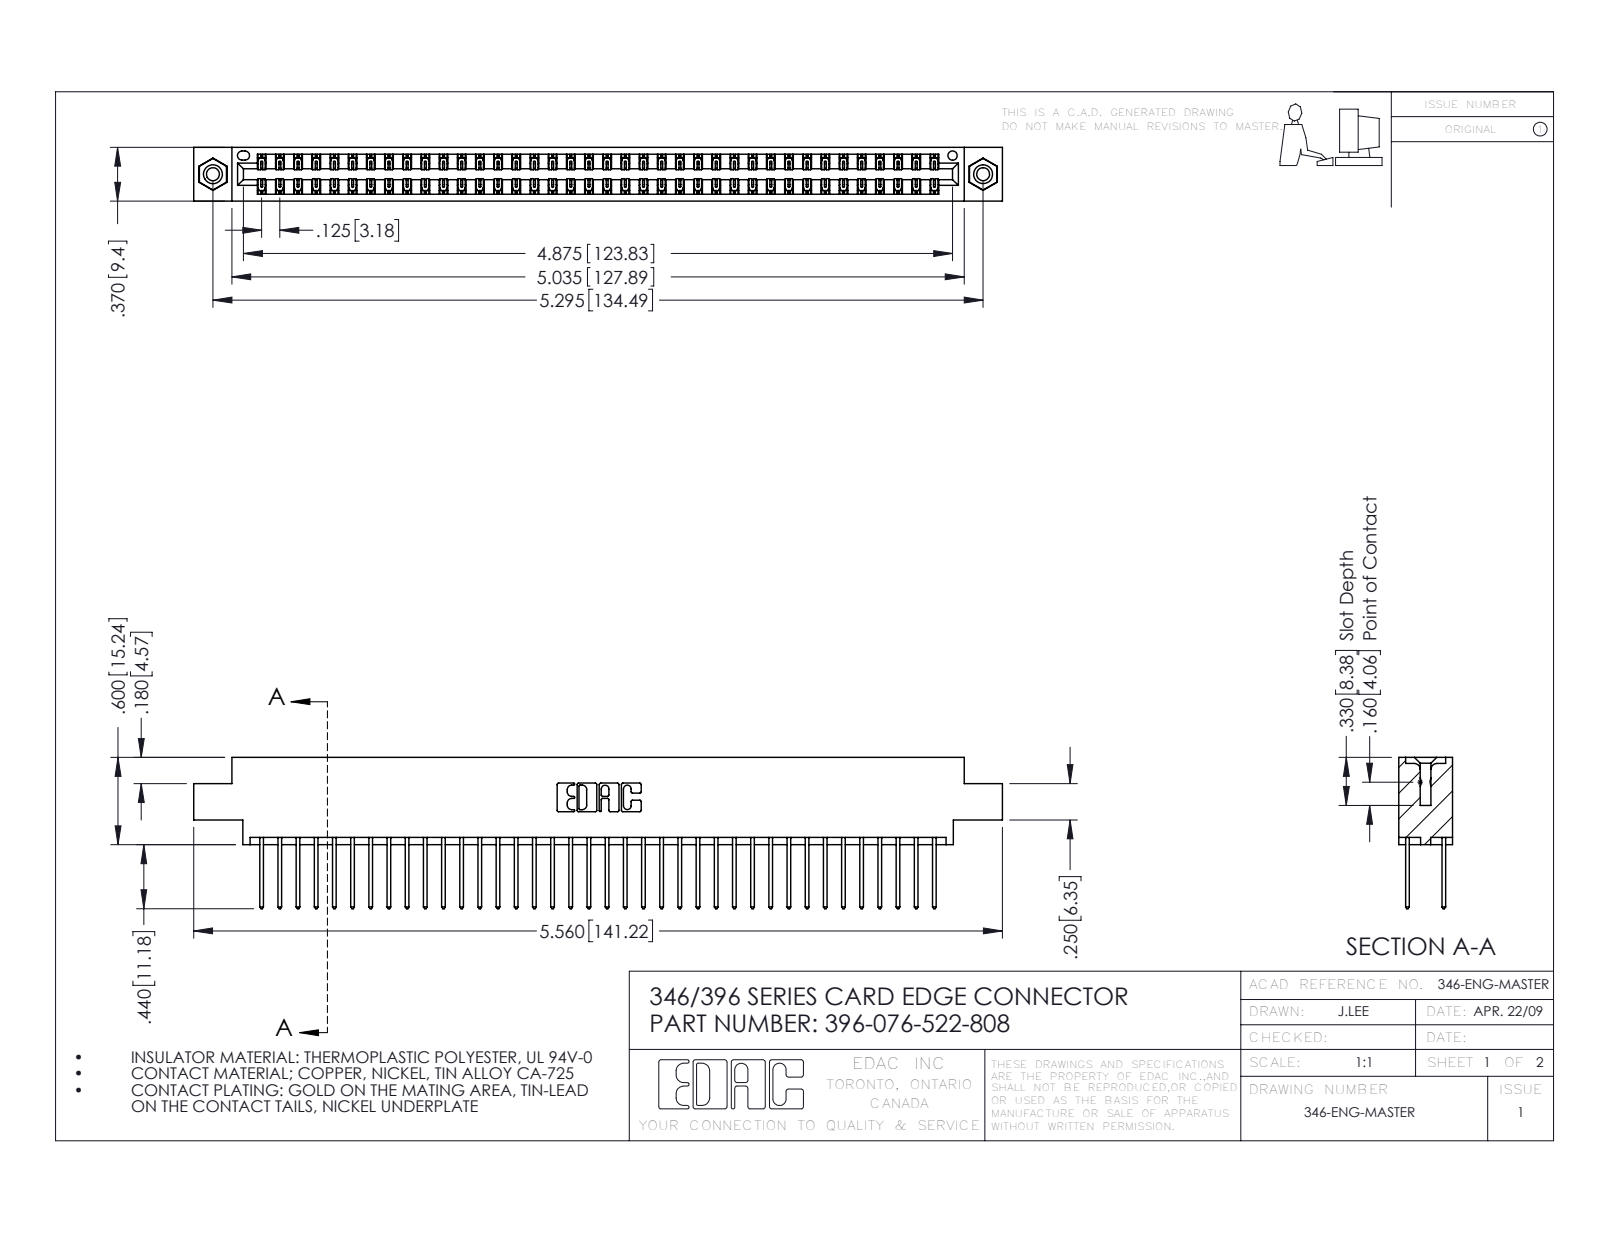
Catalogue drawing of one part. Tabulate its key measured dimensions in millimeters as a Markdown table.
| quantity | value |
| --- | --- |
| part name | 345-250-001_345-250-003-102; 396-076-522-808; 346 Part_0.170 Offset - 0.156 Dia-TI; 345-292-001_345-293-122 |
| STEP written by | SolidWorks 2016 (CONFIG_CONTROL_DESIGN) |
| units | millimeters |
| bodies | 79 solids, 4138 faces (2772 planar, 1350 cylindrical, 16 other) |
| overall size | 141.2 × 26.4 × 9.4 |
| volume | 13 800 mm³ |
| surface area | 19 970 mm² |
| round holes (diameter × count) | 2.3 × 2, 3.2 × 2, 4 × 2, 1.6 × 1 |
| round bosses / shafts (diameter × count) | 3.9 × 2 |
| partial cylindrical surfaces (radius × count) | 0.2 × 114, 0.3 × 76, 0.3 × 22, 0.2 × 6, 0.8 × 6, 0.7 × 3, 0.4 × 2, 0.6 × 2 |
| main face-to-face distances | 1.2, 8.2, 6.4, 9.4, 1.8, 7.6, 0.6, 7, 5.6, 3.8 |
| hole center spacings | 6.2, 129.2, 134.5 |
